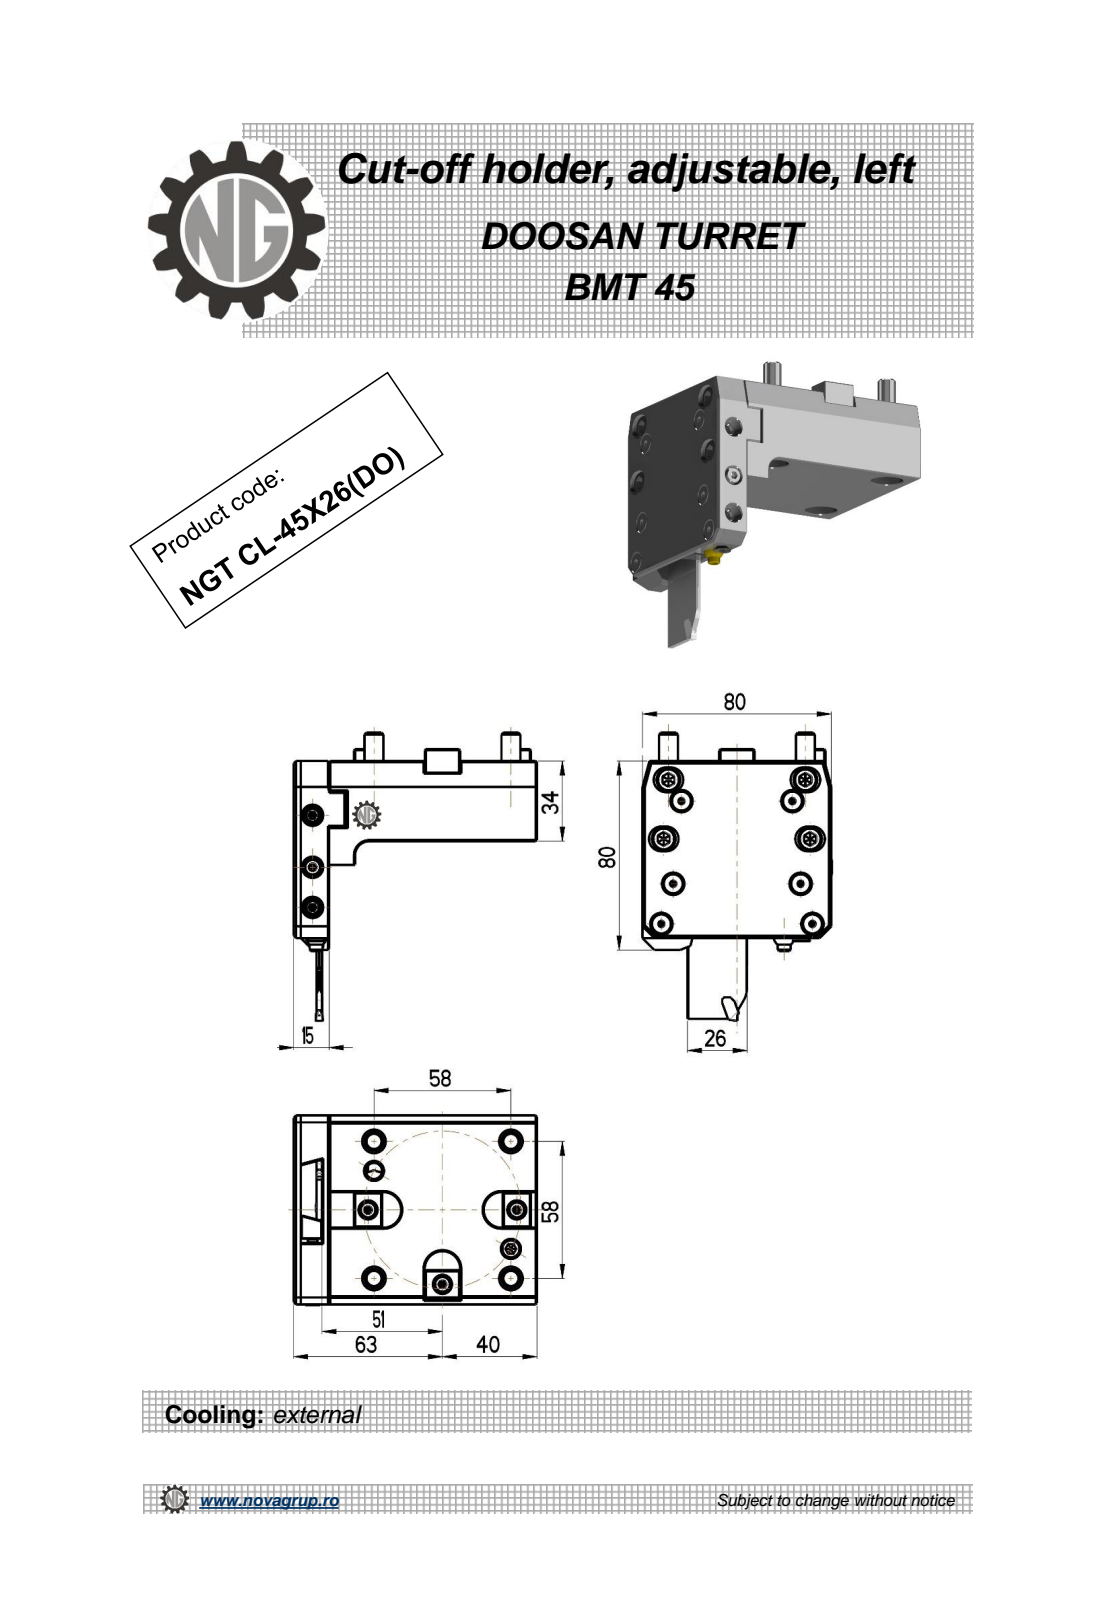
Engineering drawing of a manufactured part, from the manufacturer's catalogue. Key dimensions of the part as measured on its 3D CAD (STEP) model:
Part name (STEP PRODUCT): NGT_CL_45_26_DO
STEP written by: PRO/ENGINEER BY PARAMETRIC TECHNOLOGY CORPORATION, 2010280 (CONFIG_CONTROL_DESIGN)
Units: millimetres
Bodies: 1 solid, 421 faces (271 planar, 85 cylindrical, 65 other)
Overall size (bounding box): 103 × 92.45 × 80.26
Volume: 311 816 mm³ · Surface area: 52 092 mm²
Round holes (diameter × count): ⌀3.5 ×1, ⌀6.8 ×1
Round bosses / shafts (diameter × count): ⌀8 ×5, ⌀10 ×4, ⌀4 ×3, ⌀5.5 ×1
Partial cylindrical surfaces — rounded edges, fillets, slot ends (radius × count): R0.2 ×24, R5.25 ×8, R0.14 ×6, R0.16 ×6, R0.41 ×6, R7.5 ×3, R6 ×1, R60 ×1
Main face-to-face distances: 34, 12, 3, 15, 80, 88, 103, 100, 91, 9
Hole centre spacings: 43.96
